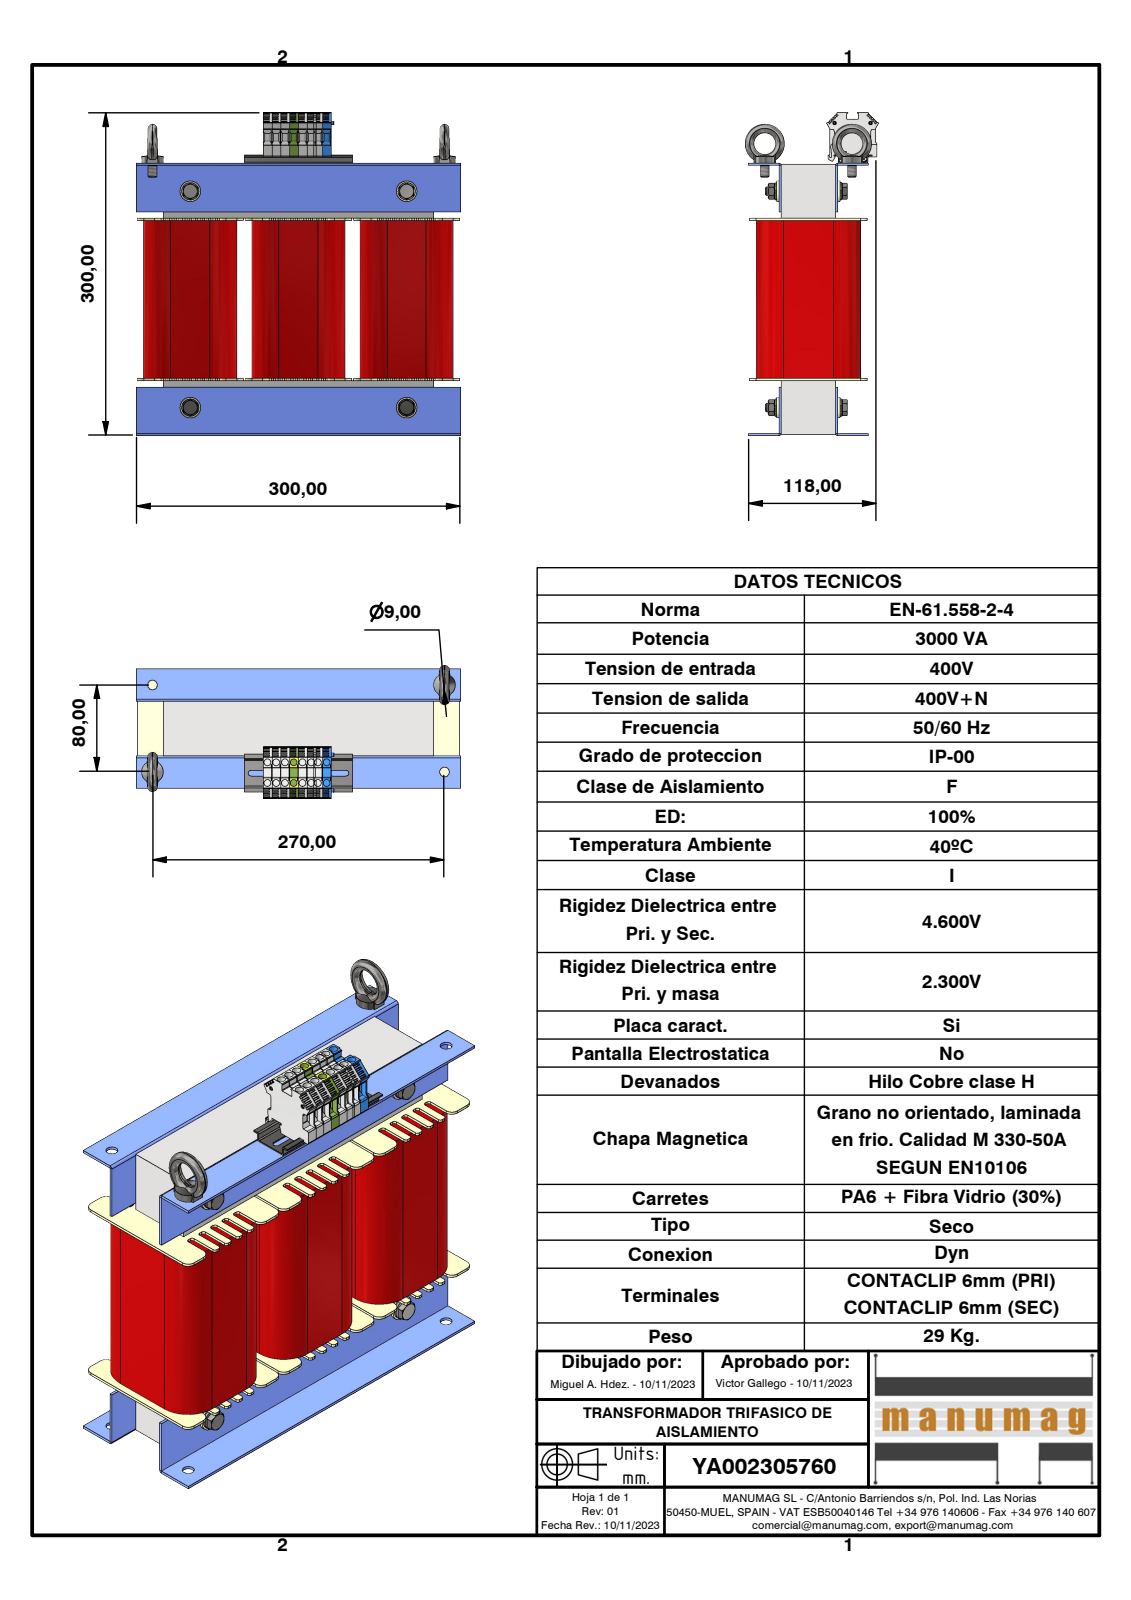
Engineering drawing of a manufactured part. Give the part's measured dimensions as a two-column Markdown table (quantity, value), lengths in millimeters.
| quantity | value |
| --- | --- |
| part name | YA002305760; 3UI150 250 x 250 - 50 (Rc50); UI 150_50; RC50 NT050 (+8 more) |
| STEP written by | Autodesk Inventor 2023 (AUTOMOTIVE_DESIGN) |
| units | millimeters |
| bodies | 43 solids, 3074 faces (2108 planar, 782 cylindrical, 184 other) |
| overall size | 300 × 299.05 × 122.6 |
| volume | 5 026 000 mm³ |
| surface area | 760 988 mm² |
| round holes (diameter × count) | 6.3 × 16, 11 × 6, 6.65 × 4, 8 × 4, 8.4 × 4, 9 × 4, 10.5 × 4, 2.4 × 2, 2.5 × 2, 2.75 × 2, 2.95 × 2, 20 × 2 |
| round bosses / shafts (diameter × count) | 19 × 4, 16 × 4, 11.4 × 4, 9.6 × 4, 7.32 × 4, 36 × 2, 8 × 2, 7 × 2 |
| partial cylindrical surfaces (radius × count) | 2 × 109, 6 × 24, 0.25 × 16, 1 × 15, 25 × 12, 2.6 × 8, 0.3 × 5, 0.5 × 5 |
| main face-to-face distances | 50, 2, 100, 52, 200, 150, 250, 51, 1, 199 |
| hole center spacings | 8.1, 20.65, 16.2, 19, 24.97, 24.3, 30.85, 200 |
